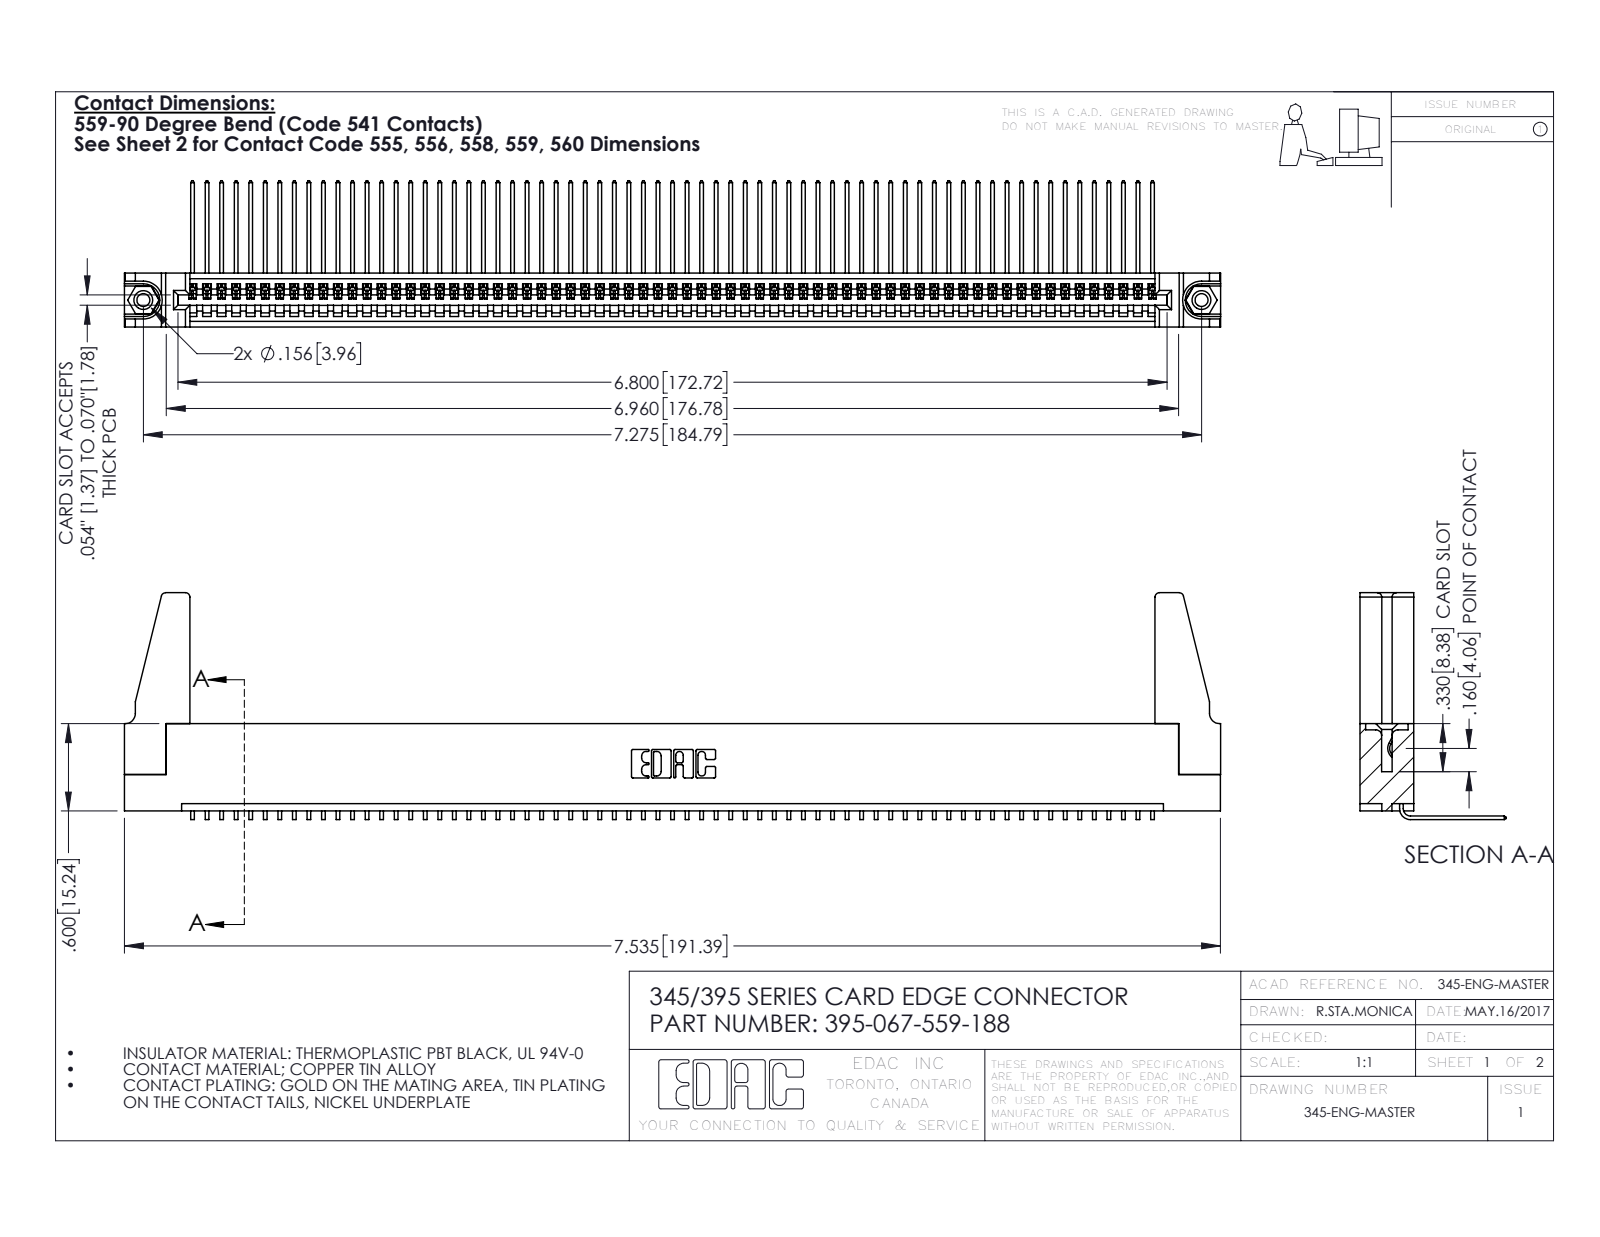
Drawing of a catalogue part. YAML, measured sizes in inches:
part_name: "395-067-559-188; 345-220-078_345-220-088; 345-250-001_345-250-001-102; 345-292-001_558 559 Tail - 1 (+1 more)"
step_written_by: "SolidWorks 2016 (CONFIG_CONTROL_DESIGN)"
units: inches
bodies: {solids: 72, faces: 4270, planar: 2966, cylindrical: 1288, other: 16}
overall_size: [7.536, 1.559, 1.005]
volume: 1.334
surface_area: 45.74
round_holes:
  - {diameter: 0.089, count: 2}
  - {diameter: 0.125, count: 2}
  - {diameter: 0.156, count: 2}
  - {diameter: 0.064, count: 1}
round_bosses_or_shafts:
  - {diameter: 0.155, count: 2}
partial_cylinders:
  - {radius: 0.006, count: 134}
  - {radius: 0.01, count: 22}
  - {radius: 0.03, count: 8}
  - {radius: 0.007, count: 6}
  - {radius: 0.031, count: 6}
  - {radius: 0.026, count: 3}
  - {radius: 0.031, count: 2}
  - {radius: 0.04, count: 2}
face_to_face_distances: [0.072, 0.298, 0.37, 0.2, 0.098, 0.272, 0.025, 0.225, 0.149, 0.072]
hole_center_spacings: [0.27, 7.039, 7.275]
